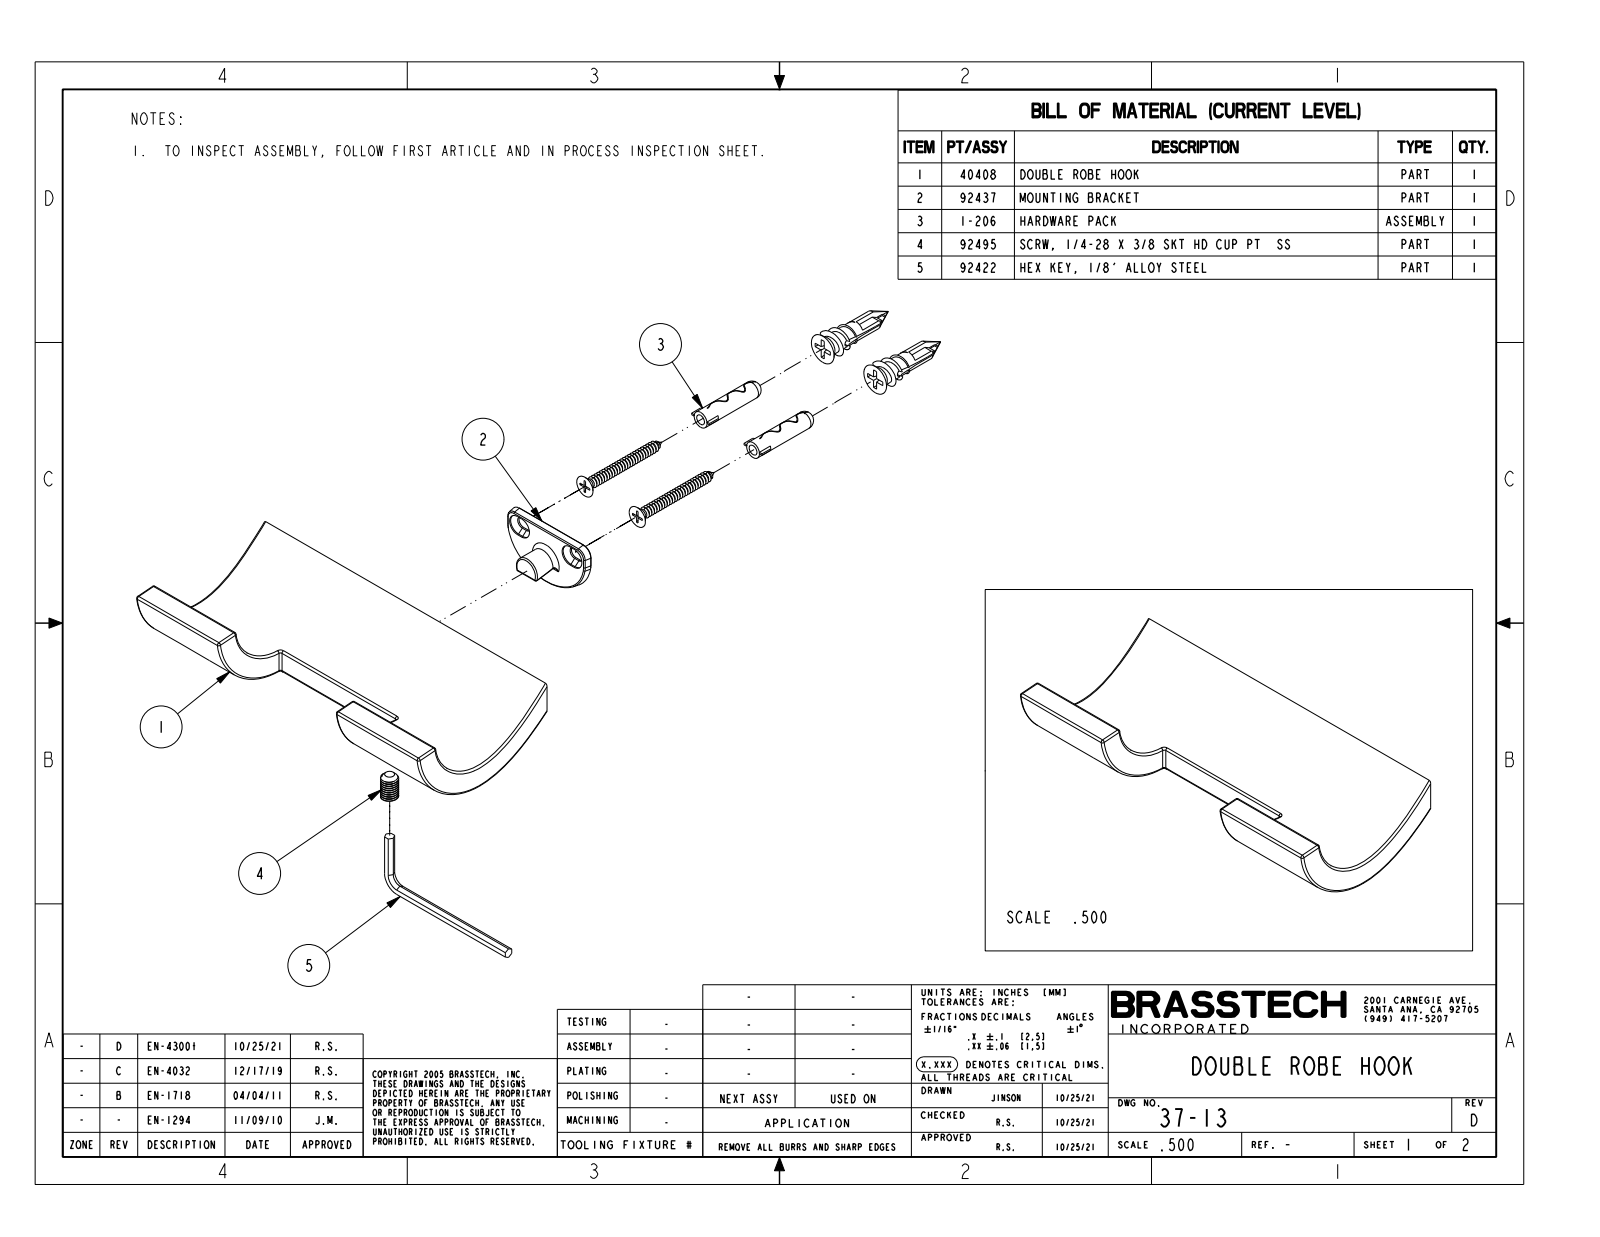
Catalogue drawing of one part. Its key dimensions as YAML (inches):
part_name: "37-13"
step_written_by: "CREO PARAMETRIC BY PTC INC, 2018400 (CONFIG_CONTROL_DESIGN)"
units: inches
bodies: {solids: 1, faces: 48, planar: 8, cylindrical: 6, other: 34}
overall_size: [5.5, 2.517, 1.08]
volume: 5.531
surface_area: 34.87
partial_cylinders:
  - {radius: 0.03, count: 6}
face_to_face_distances: [5.5, 1.617, 3.883, 1.3, 2.265]
